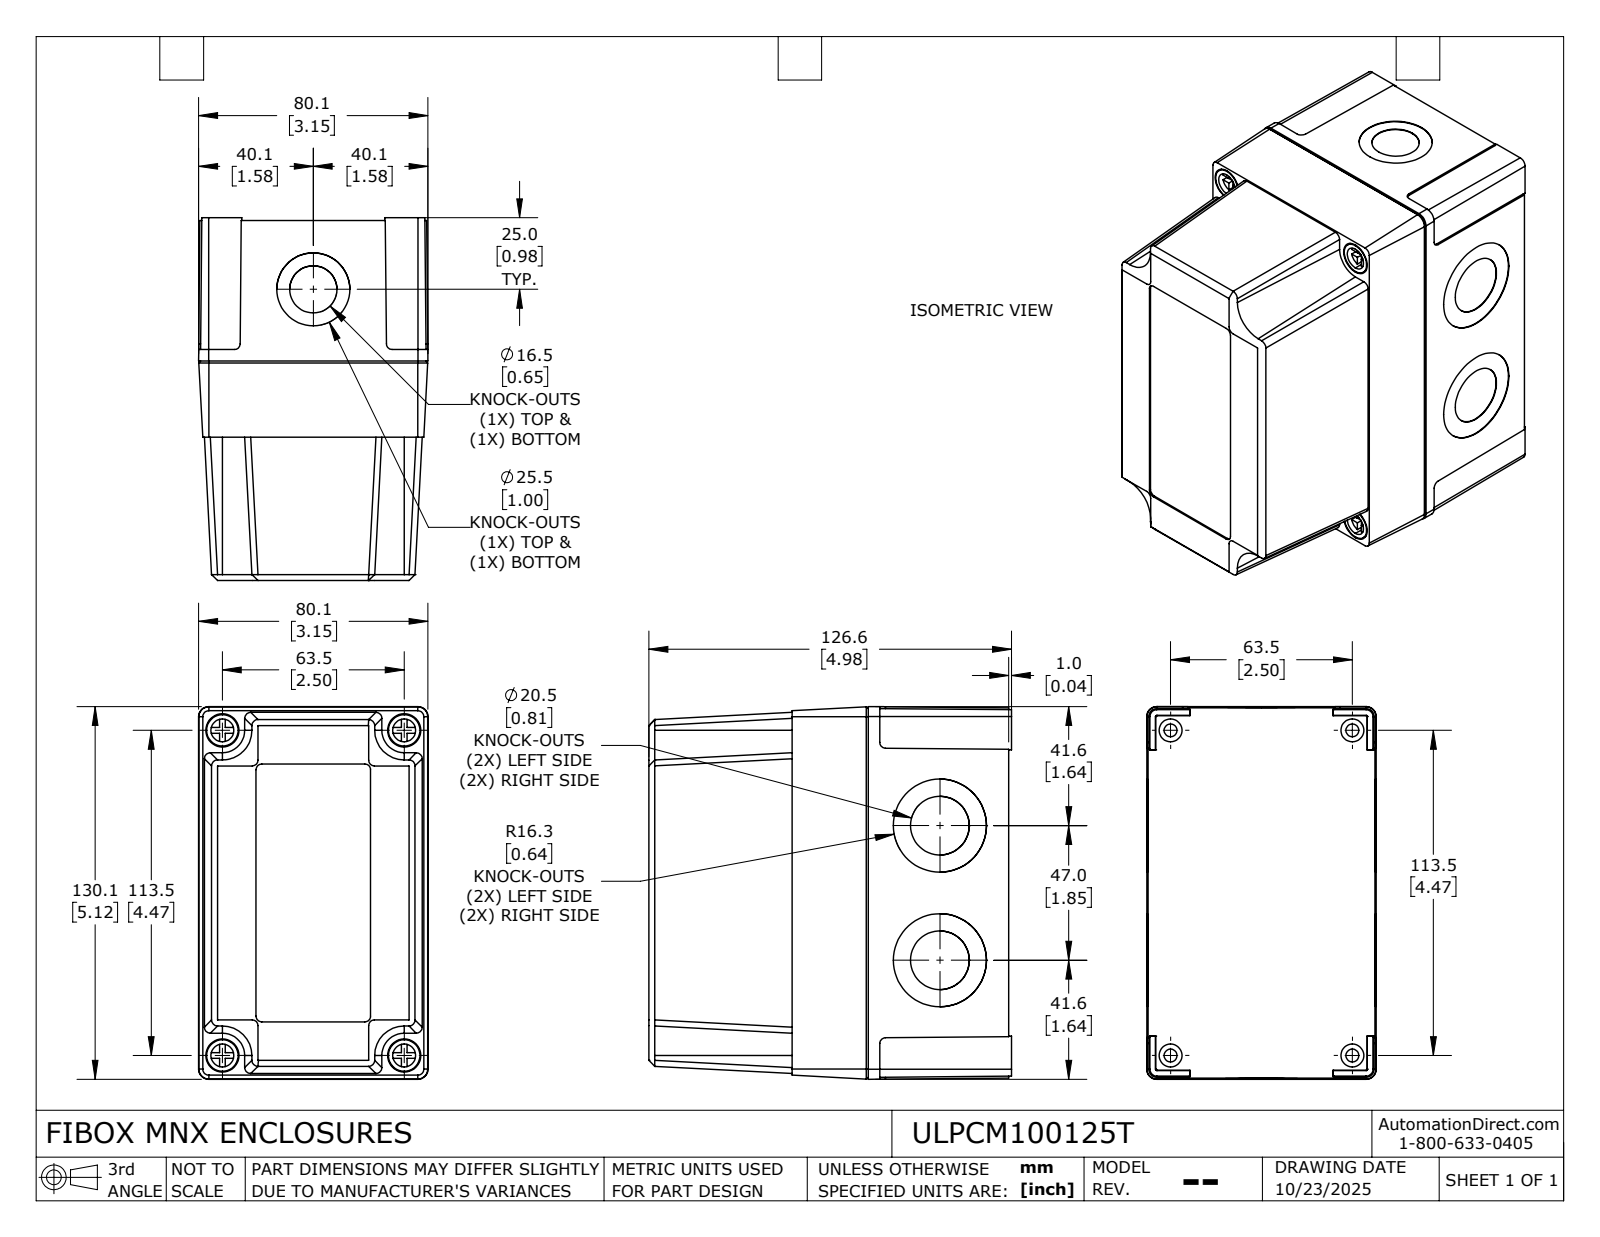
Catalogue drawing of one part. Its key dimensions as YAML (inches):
part_name: "ULPCM100125T_Default"
step_written_by: "SolidWorks 2024 (CONFIG_CONTROL_DESIGN)"
units: inches
bodies: {solids: 6, faces: 565, planar: 331, cylindrical: 184, other: 50}
overall_size: [5.122, 4.984, 3.154]
volume: 13.27
surface_area: 231
round_holes:
  - {diameter: 0.126, count: 8}
  - {diameter: 0.157, count: 8}
  - {diameter: 0.177, count: 4}
  - {diameter: 0.315, count: 4}
  - {diameter: 0.457, count: 4}
  - {diameter: 0.807, count: 4}
  - {diameter: 1.28, count: 4}
  - {diameter: 0.65, count: 2}
  - {diameter: 1.004, count: 2}
round_bosses_or_shafts:
  - {diameter: 0.315, count: 8}
  - {diameter: 0.098, count: 8}
  - {diameter: 0.433, count: 4}
  - {diameter: 0.283, count: 4}
partial_cylinders:
  - {radius: 0.079, count: 8}
  - {radius: 0.083, count: 8}
  - {radius: 0.056, count: 6}
  - {radius: 0.021, count: 4}
  - {radius: 0.197, count: 4}
  - {radius: 0.023, count: 2}
face_to_face_distances: [0.055, 0.165, 0.118, 4.854, 4.736, 0.077, 0.022, 0.026, 0.139, 0.078]
hole_center_spacings: [0.841, 0.888, 1.333, 1.476, 1.939, 2.159, 2.174, 2.281]
